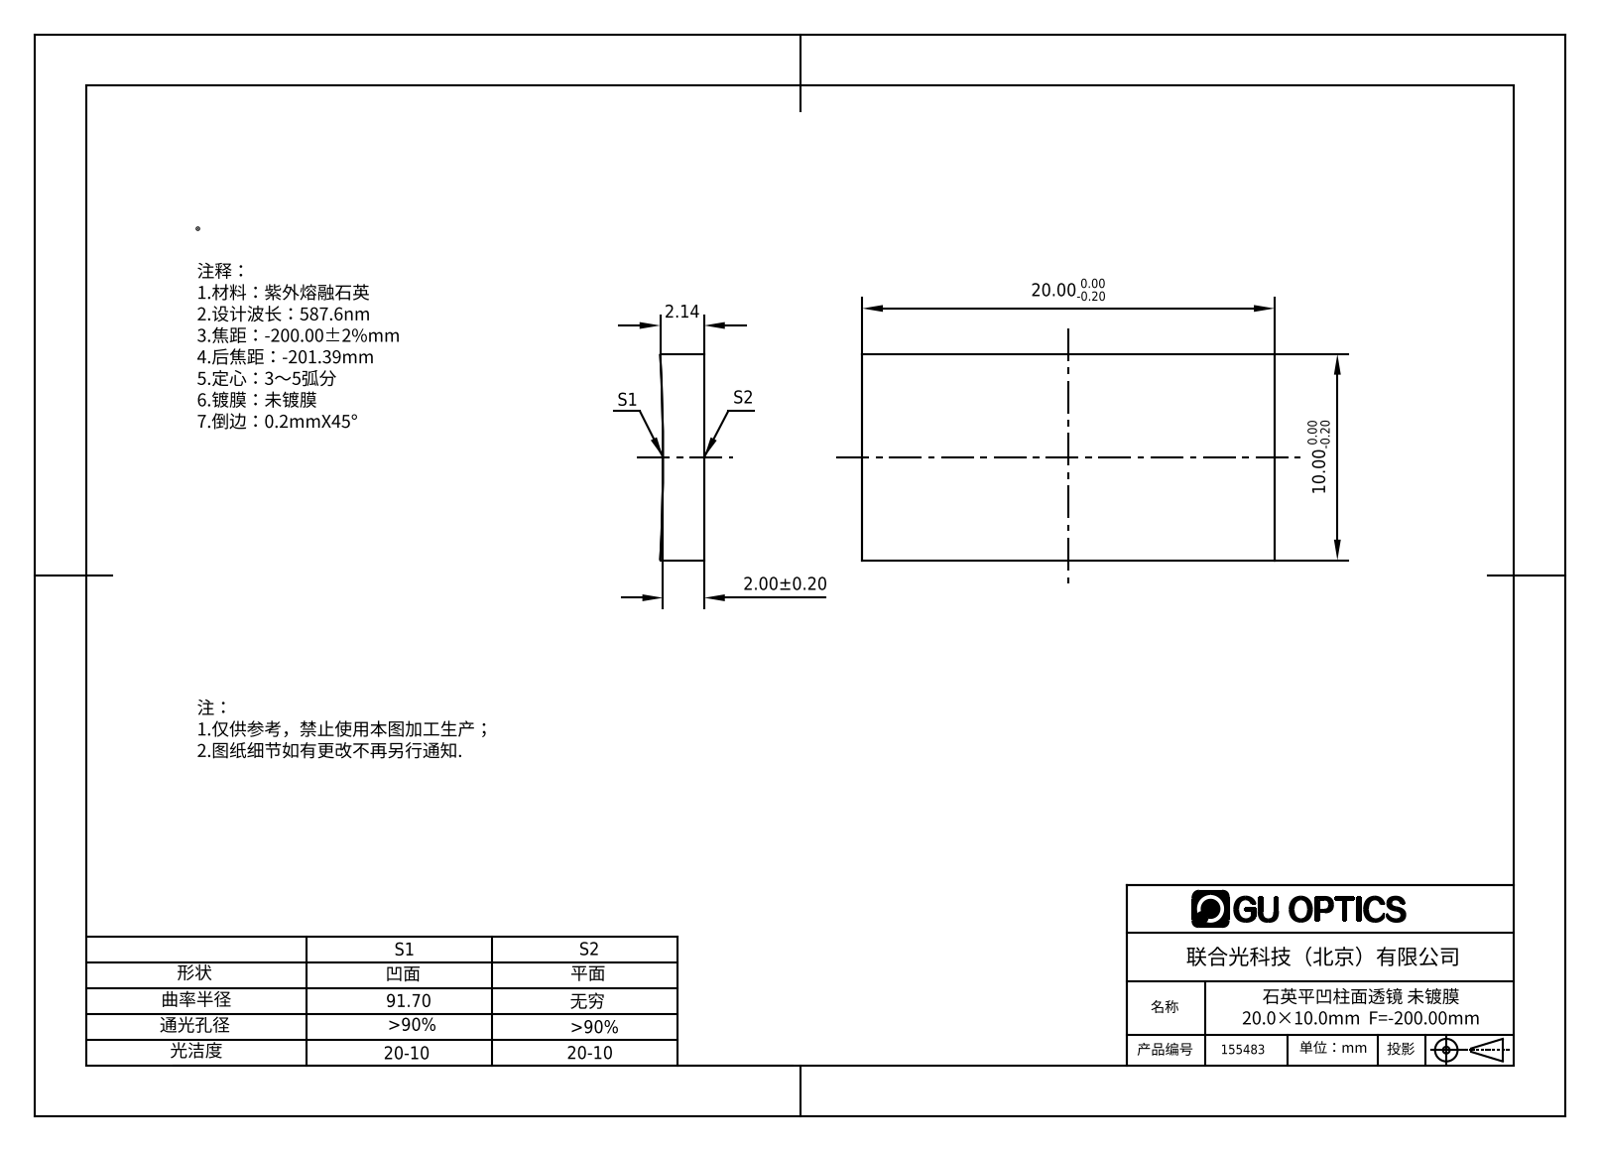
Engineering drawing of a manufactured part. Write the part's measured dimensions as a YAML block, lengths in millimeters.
part_name: "155483"
step_written_by: "SolidWorks 2016 (AUTOMOTIVE_DESIGN)"
units: millimeters
bodies: {solids: 1, faces: 6, planar: 5, cylindrical: 1, other: 0}
overall_size: [20, 10, 2.14]
volume: 409
surface_area: 526
partial_cylinders:
  - {radius: 91.7, count: 1}
face_to_face_distances: [10, 20]
